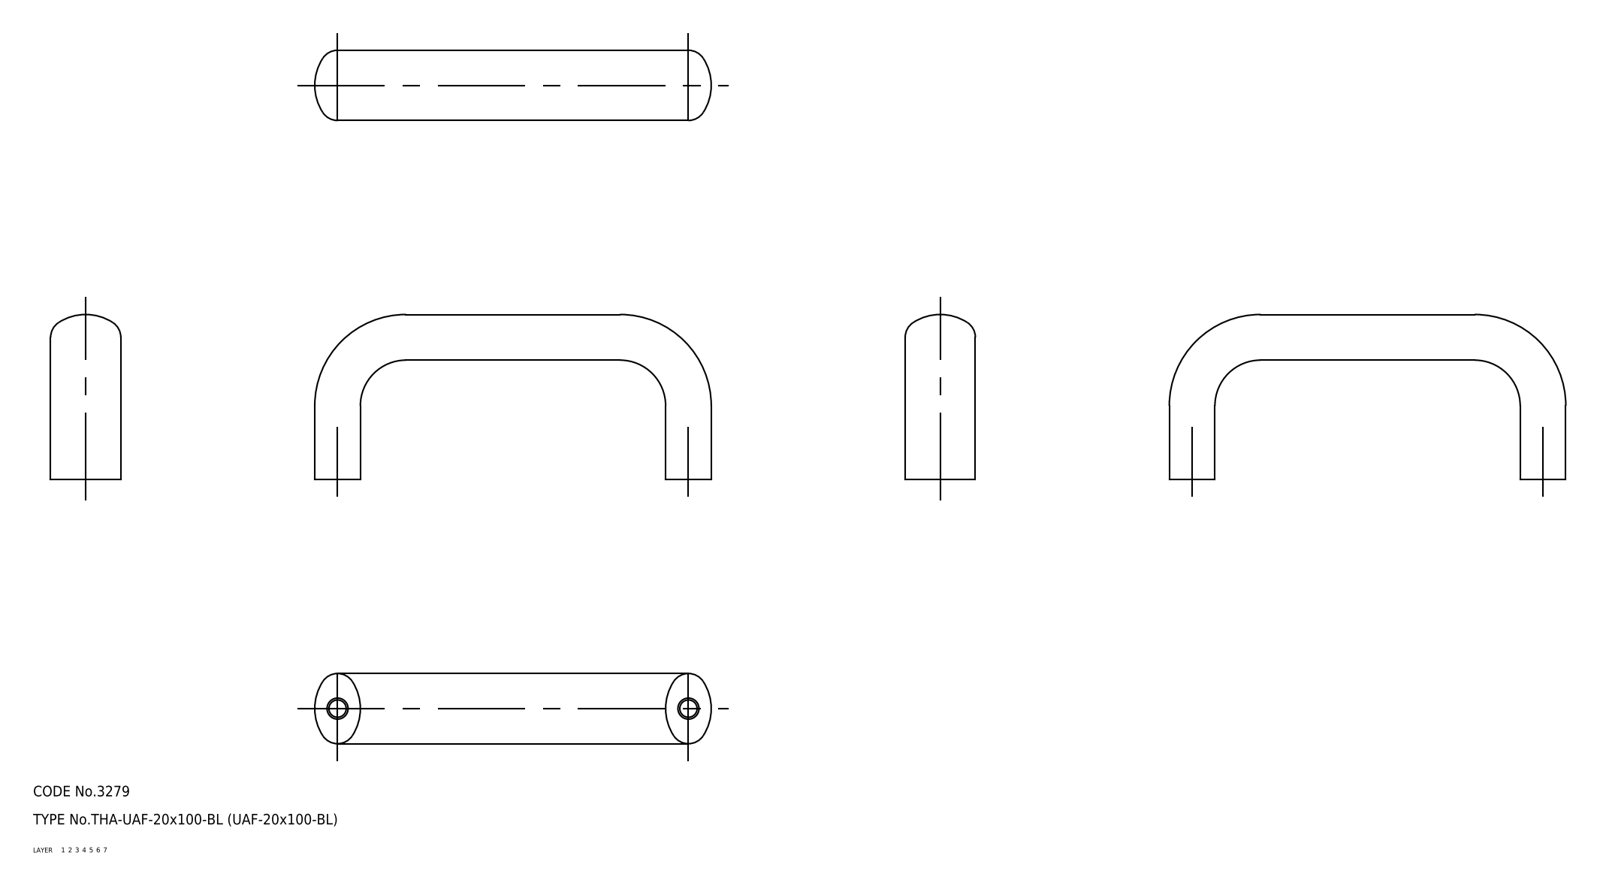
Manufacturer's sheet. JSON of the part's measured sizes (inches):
{"part_name": "pull", "step_written_by": "CADfix (AUTOMOTIVE_DESIGN)", "units": "inches", "bodies": {"solids": 1, "faces": 18, "planar": 0, "cylindrical": 0, "other": 18}, "overall_size": [4.449, 1.85, 0.787], "volume_in3": 2.01, "surface_area_in2": 14.56}
